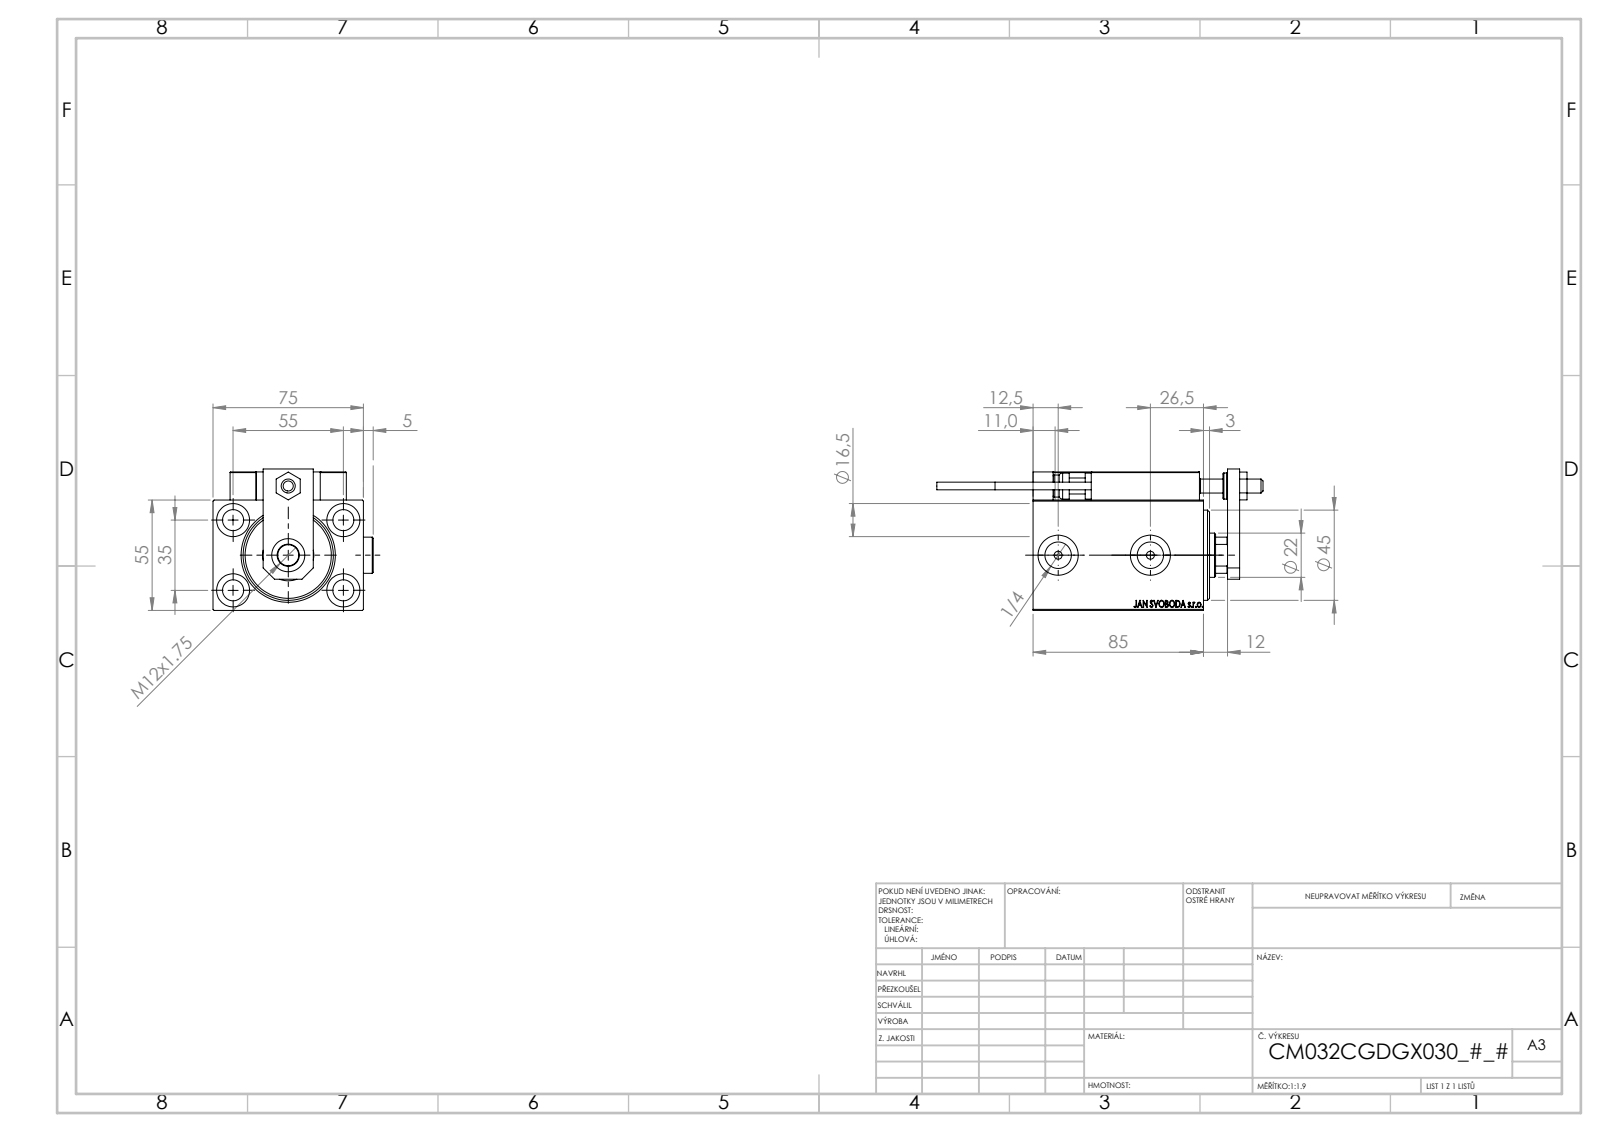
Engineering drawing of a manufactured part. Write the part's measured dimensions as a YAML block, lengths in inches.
part_name: "ALLEN BOLT D8; MAGNET; ZARAZKA; Block (+7 more)"
step_written_by: "SolidWorks 2019 (CONFIG_CONTROL_DESIGN)"
units: inches
bodies: {solids: 25, faces: 1336, planar: 594, cylindrical: 204, other: 538}
overall_size: [6.406, 3.146, 2.776]
volume: 21.1
surface_area: 144.6
round_holes:
  - {diameter: 0.157, count: 6}
  - {diameter: 0.315, count: 5}
  - {diameter: 0.413, count: 5}
  - {diameter: 0.65, count: 5}
  - {diameter: 0.126, count: 4}
  - {diameter: 0.197, count: 2}
  - {diameter: 0.518, count: 2}
  - {diameter: 0.787, count: 2}
  - {diameter: 0.276, count: 1}
  - {diameter: 0.866, count: 1}
  - {diameter: 1.004, count: 1}
  - {diameter: 1.26, count: 1}
round_bosses_or_shafts:
  - {diameter: 0.709, count: 2}
  - {diameter: 0.197, count: 2}
  - {diameter: 0.15, count: 2}
  - {diameter: 0.512, count: 1}
  - {diameter: 0.433, count: 1}
partial_cylinders:
  - {radius: 0.012, count: 30}
  - {radius: 0.118, count: 2}
  - {radius: 0.413, count: 1}
face_to_face_distances: [2.165, 2.953, 0.551, 0.394, 0.472, 2.717, 0.197, 0.276, 0.984, 0.591]
hole_center_spacings: [1.283, 0.448, 0.787, 1.165, 1.169, 1.273, 1.378, 1.42]
